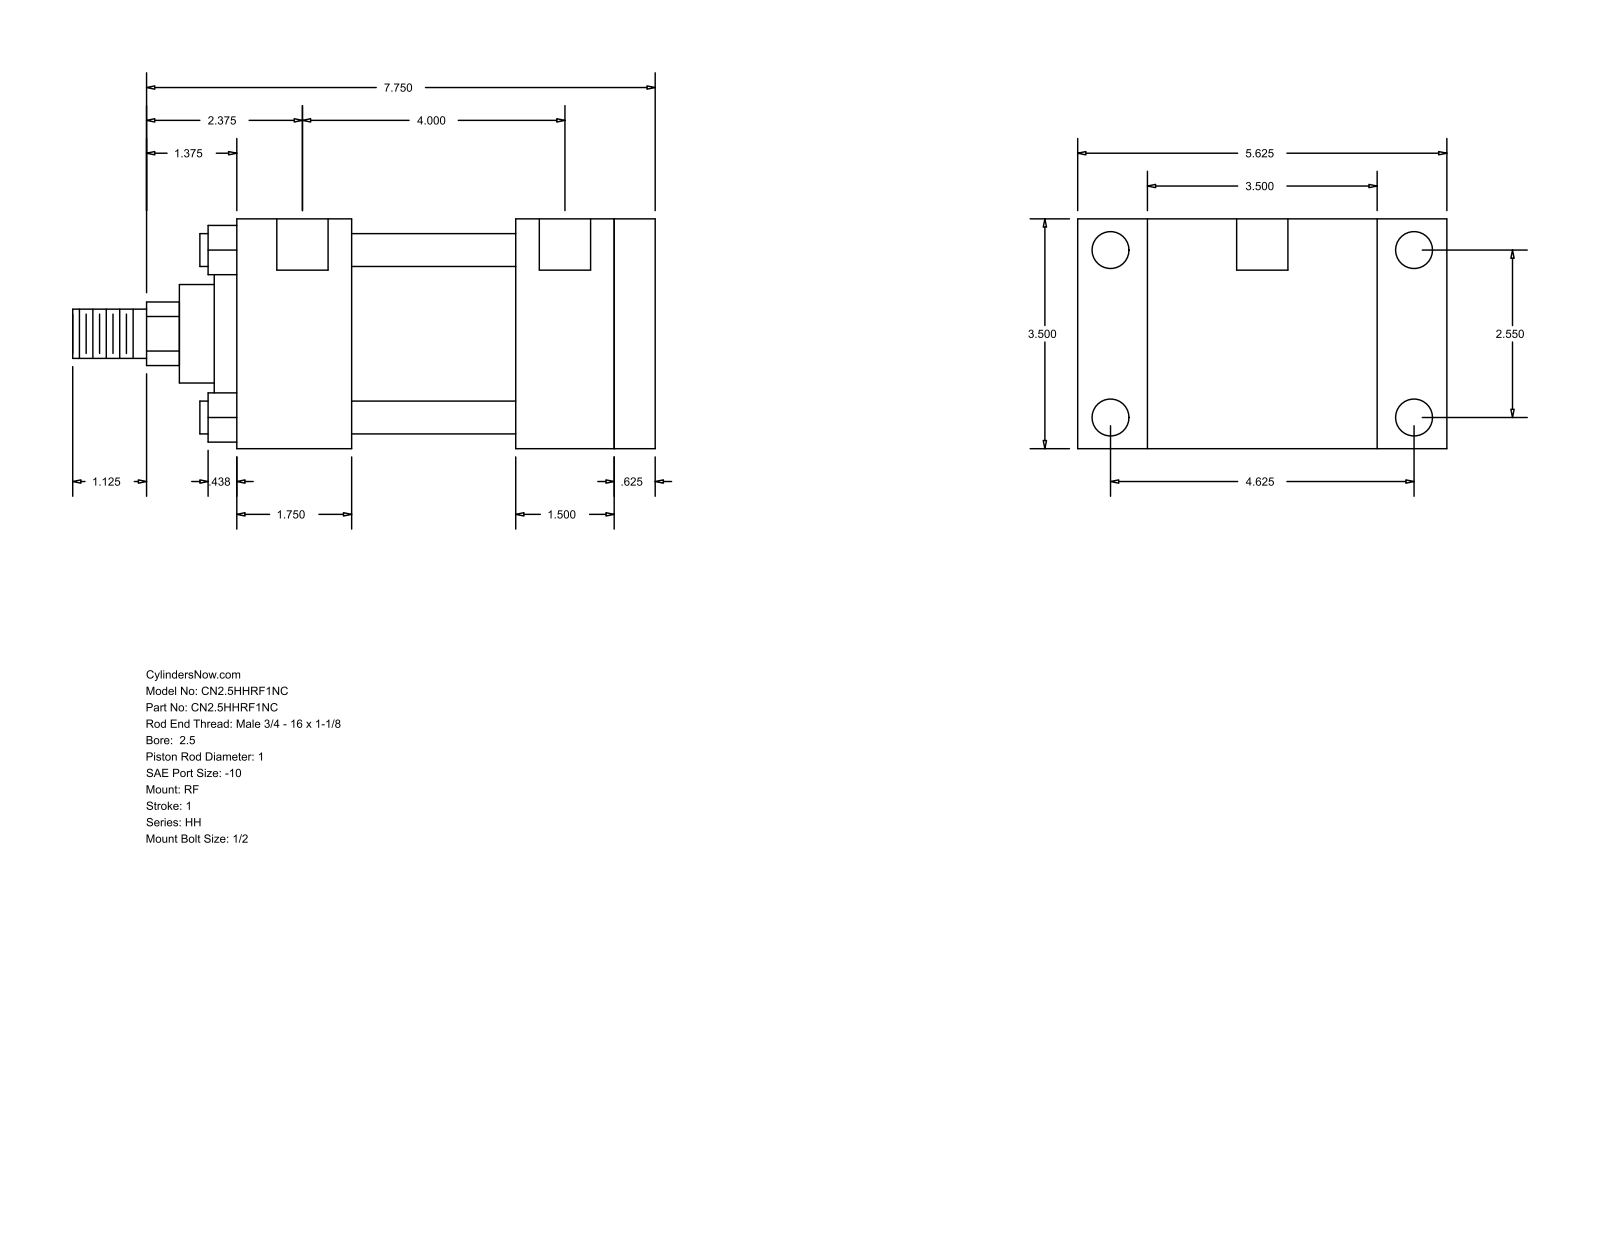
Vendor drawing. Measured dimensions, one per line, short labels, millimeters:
name: HH_RF__0250_1
written by: GSSL Pune (CONFIG_CONTROL_DESIGN)
unit: mm
bodies: 0 solids, 94 faces (65 planar, 29 cylindrical, 0 other)
size: 225.43 × 142.88 × 88.9
holes: 4× ⌀5.56, 4× ⌀14.3, 2× ⌀19.84
bosses: 4× ⌀12.7, 1× ⌀73.03, 1× ⌀60.33, 1× ⌀38.1, 1× ⌀25.4, 1× ⌀19.05
rounds: 1× R12.29
face distances: 88.9, 15.88, 146.05, 161.93, 44.46, 101.59, 117.47, 107.96, 63.5, 38.09
hole spacings: 64.76, 104.77, 117.48, 134.15, 1.58, 1.59, 101.6, 103.18
